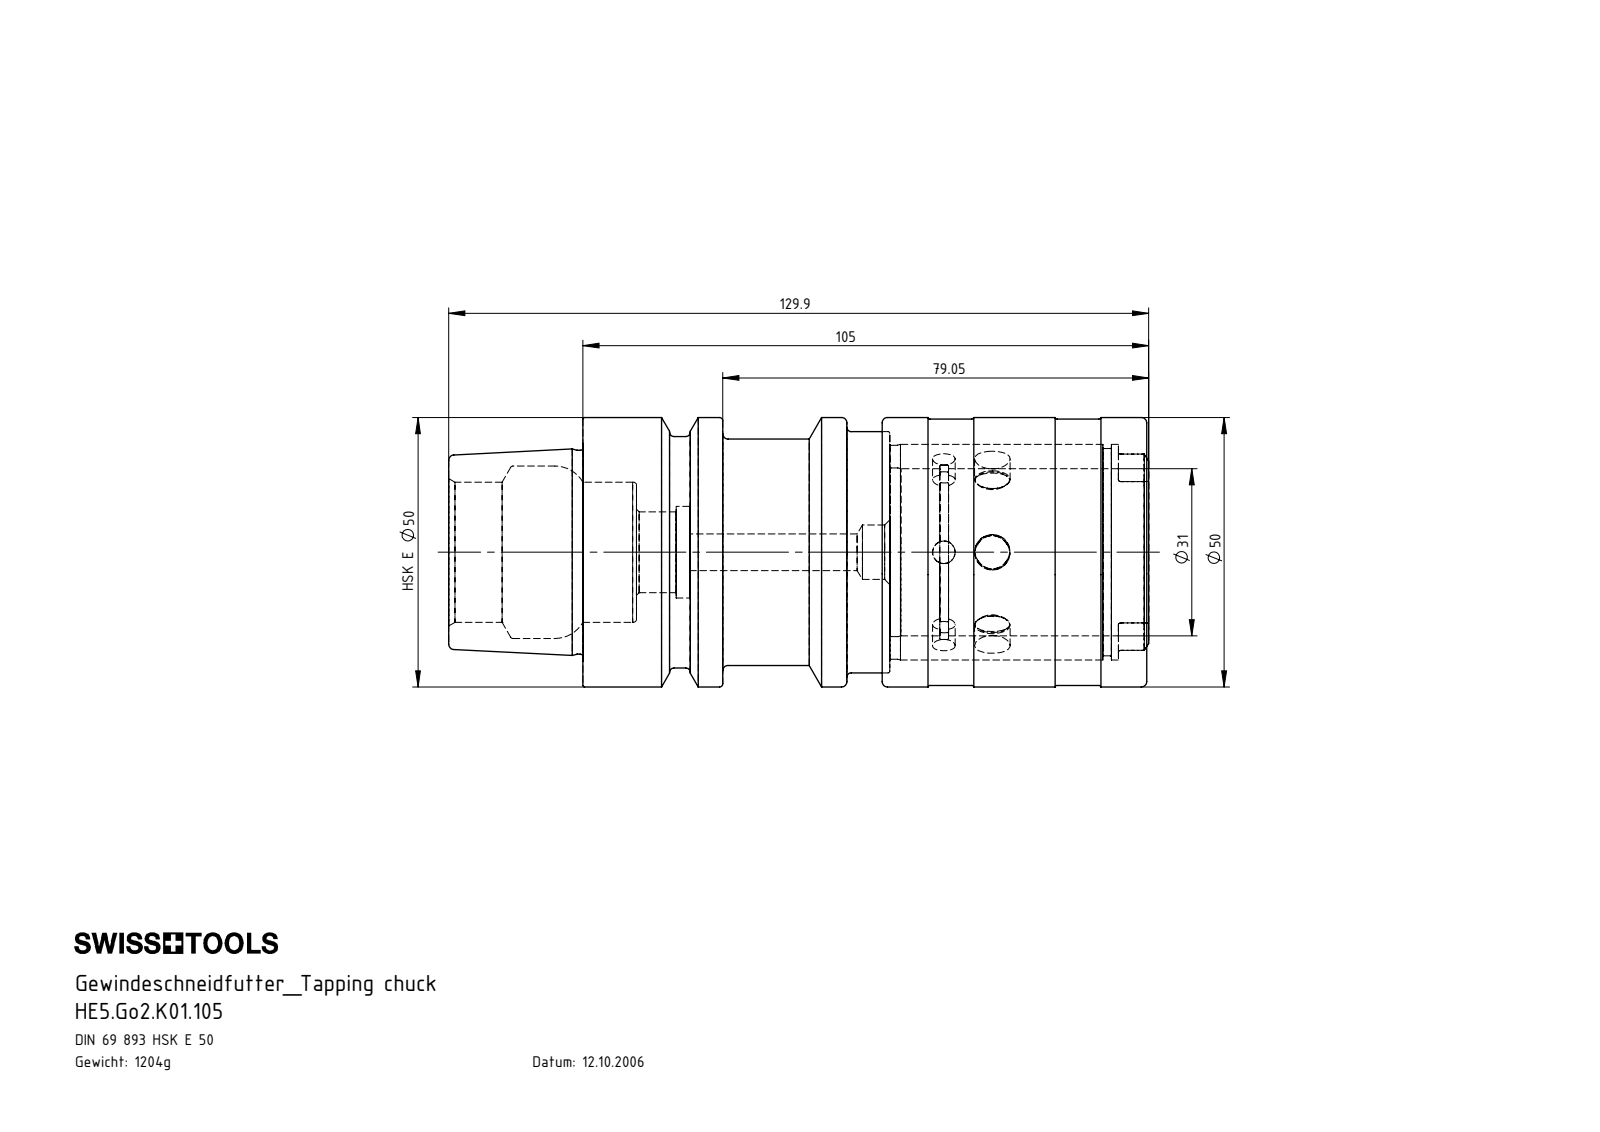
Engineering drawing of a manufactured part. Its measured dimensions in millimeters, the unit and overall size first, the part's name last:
Units: millimetres
Overall size (bounding box): 129.9 × 50 × 50
Round holes (diameter × count): ⌀4.2 ×3, ⌀6.6 ×3, ⌀2.5 ×1, ⌀6.8 ×1, ⌀10.1 ×1, ⌀15 ×1, ⌀17 ×1, ⌀26 ×1, ⌀31 ×1, ⌀31.3 ×1, ⌀32 ×1, ⌀32.35 ×1
Round bosses / shafts (diameter × count): ⌀50 ×1, ⌀49.4 ×1, ⌀44.75 ×1, ⌀42.95 ×1, ⌀42 ×1, ⌀40 ×1, ⌀39.7 ×1, ⌀38.45 ×1
Partial cylindrical surfaces — rounded edges, fillets, slot ends (radius × count): R3.1 ×3, R0.5 ×2
Main face-to-face distances: 12.65, 57, 69.65, 37.15, 57.65, 0.65, 12, 56.95, 0.7, 12.7
Hole centre spacings: 9
Volume: 153 247 mm³ · Surface area: 55 160 mm²
Bodies: 10 solids, 301 faces (51 planar, 99 cylindrical, 151 other)
Part name (STEP PRODUCT): HE5.Go2.K01.105; Einbausatz Go2_gespannt; Kugel Go2; Hülse Go2 (+6 more)
STEP written by: SolidWorks 2011 (AUTOMOTIVE_DESIGN)
